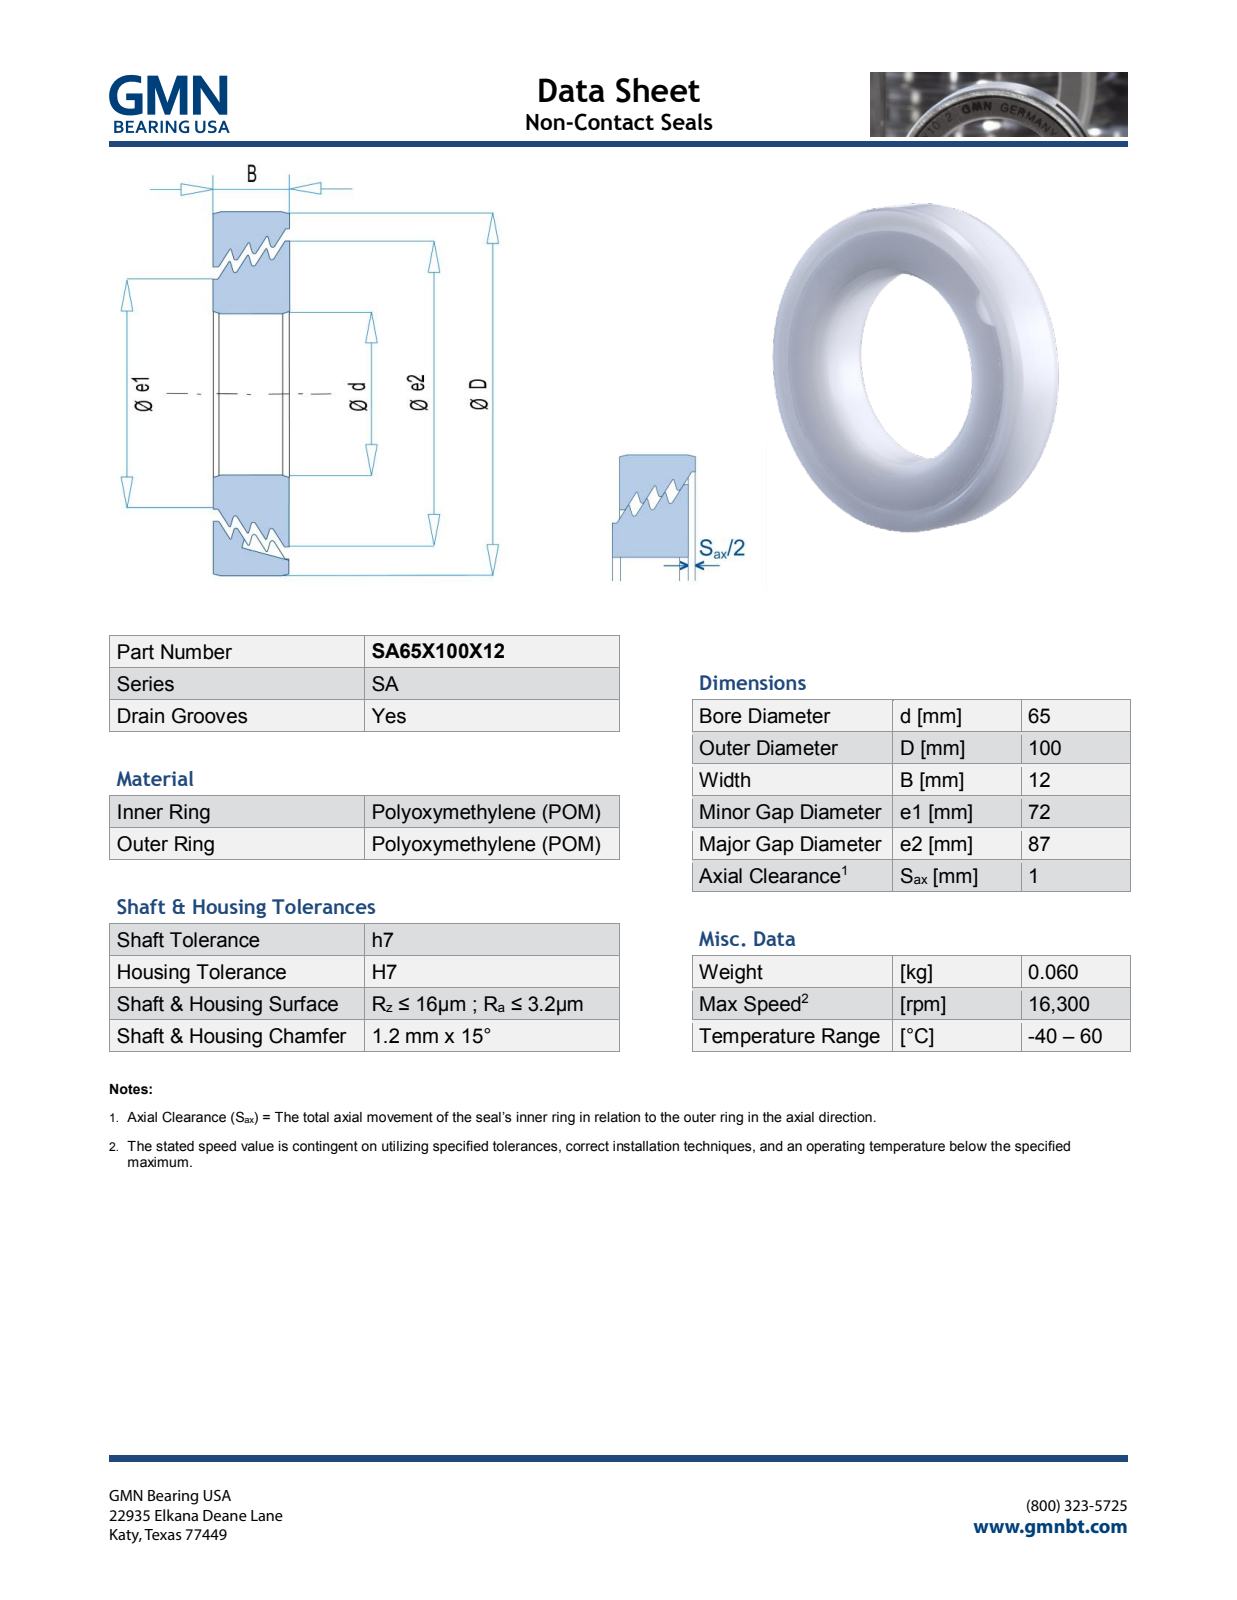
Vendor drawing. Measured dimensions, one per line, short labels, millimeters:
name: SA65X100X12_PRT
written by: PRO/ENGINEER BY PARAMETRIC TECHNOLOGY CORPORATION, 2013150 (AUTOMOTIVE_DESIGN)
unit: mm
bodies: 2 solids, 686 faces (613 planar, 13 cylindrical, 60 other)
size: 100 × 100 × 12.07
volume: 51 749 mm³; area: 27 080 mm²
holes: 1× ⌀65, 1× ⌀73.63, 1× ⌀88.63
bosses: 1× ⌀100, 1× ⌀87, 1× ⌀72
rounds: 1× R6
face distances: 12, 12.07, 6.55, 6.48, 5.52, 0.38, 3.03, 2.65, 0.39, 0.32
